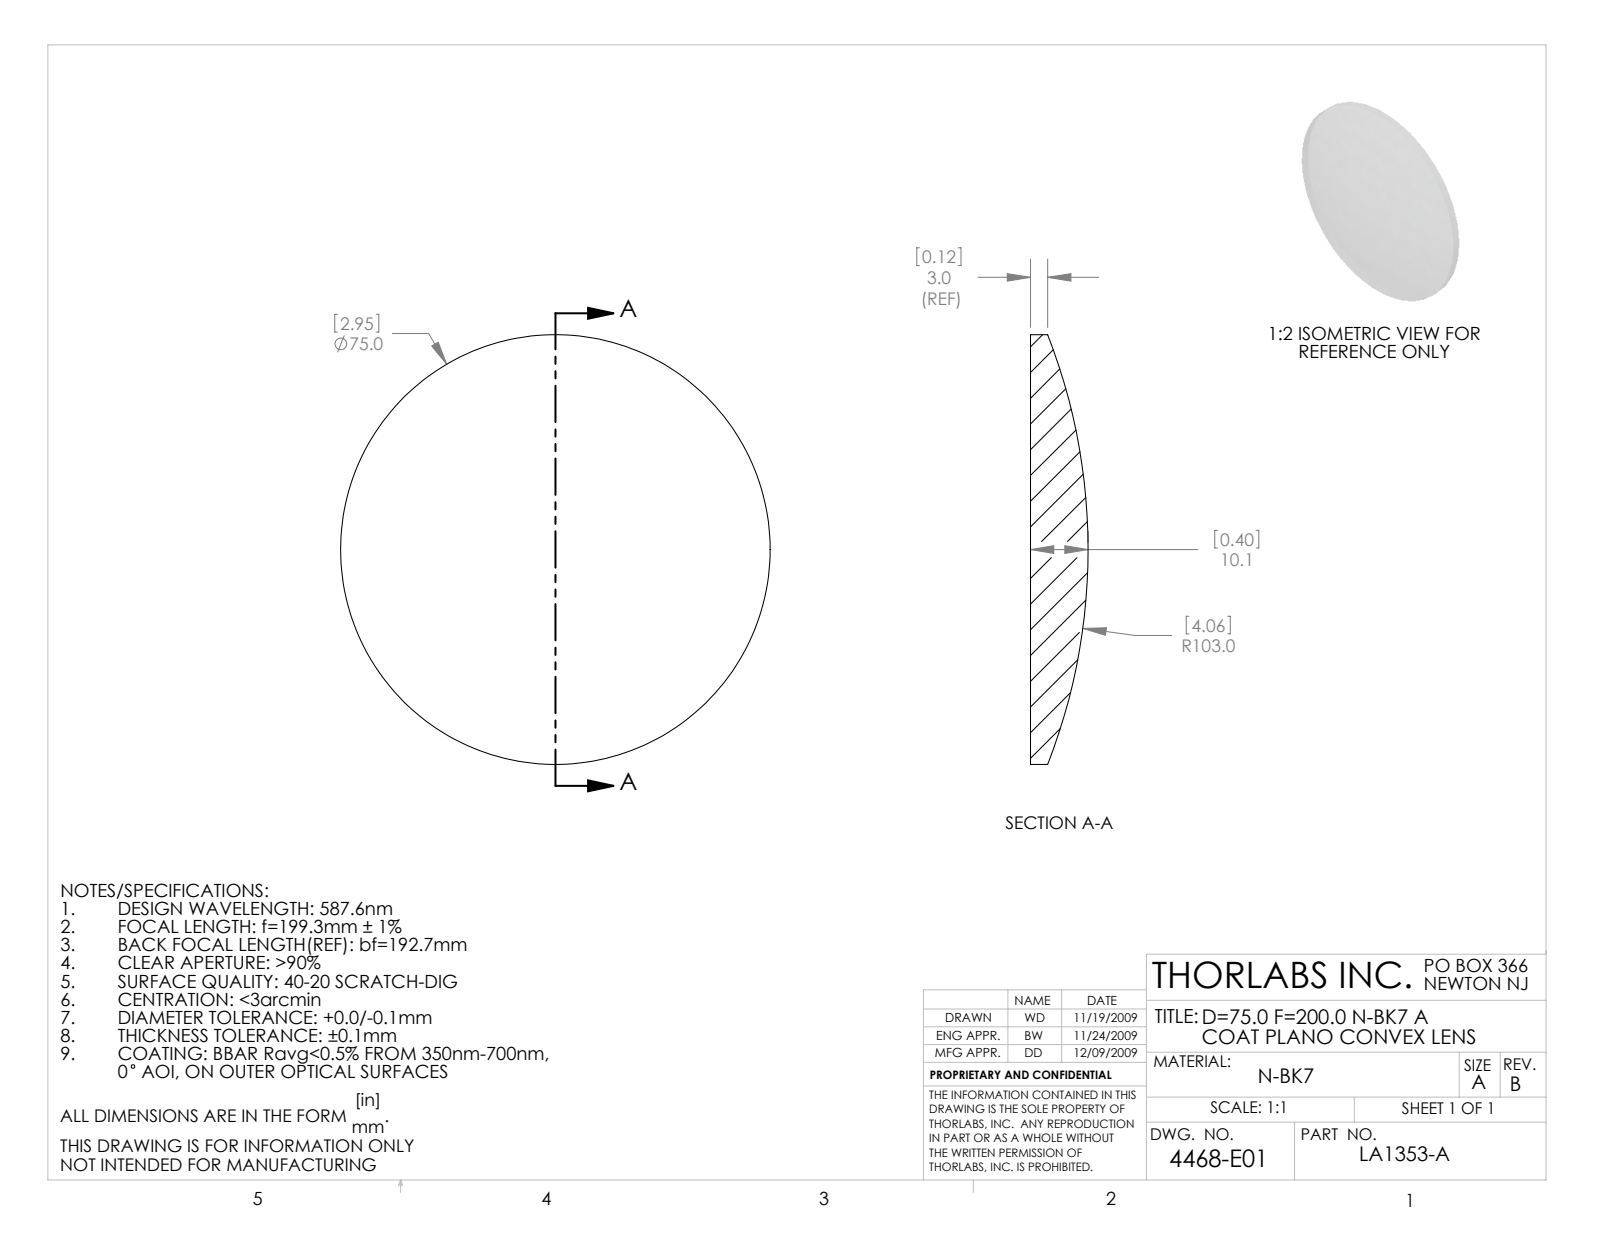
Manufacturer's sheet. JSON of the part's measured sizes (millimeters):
{"part_name": "4468-E0W", "step_written_by": "SolidWorks 2009 (AUTOMOTIVE_DESIGN)", "units": "millimeters", "bodies": {"solids": 1, "faces": 5, "planar": 1, "cylindrical": 2, "other": 2}, "overall_size": [75, 75, 10.06], "volume_mm3": 29015, "surface_area_mm2": 9698, "round_bosses_or_shafts": [[75, 1]]}
